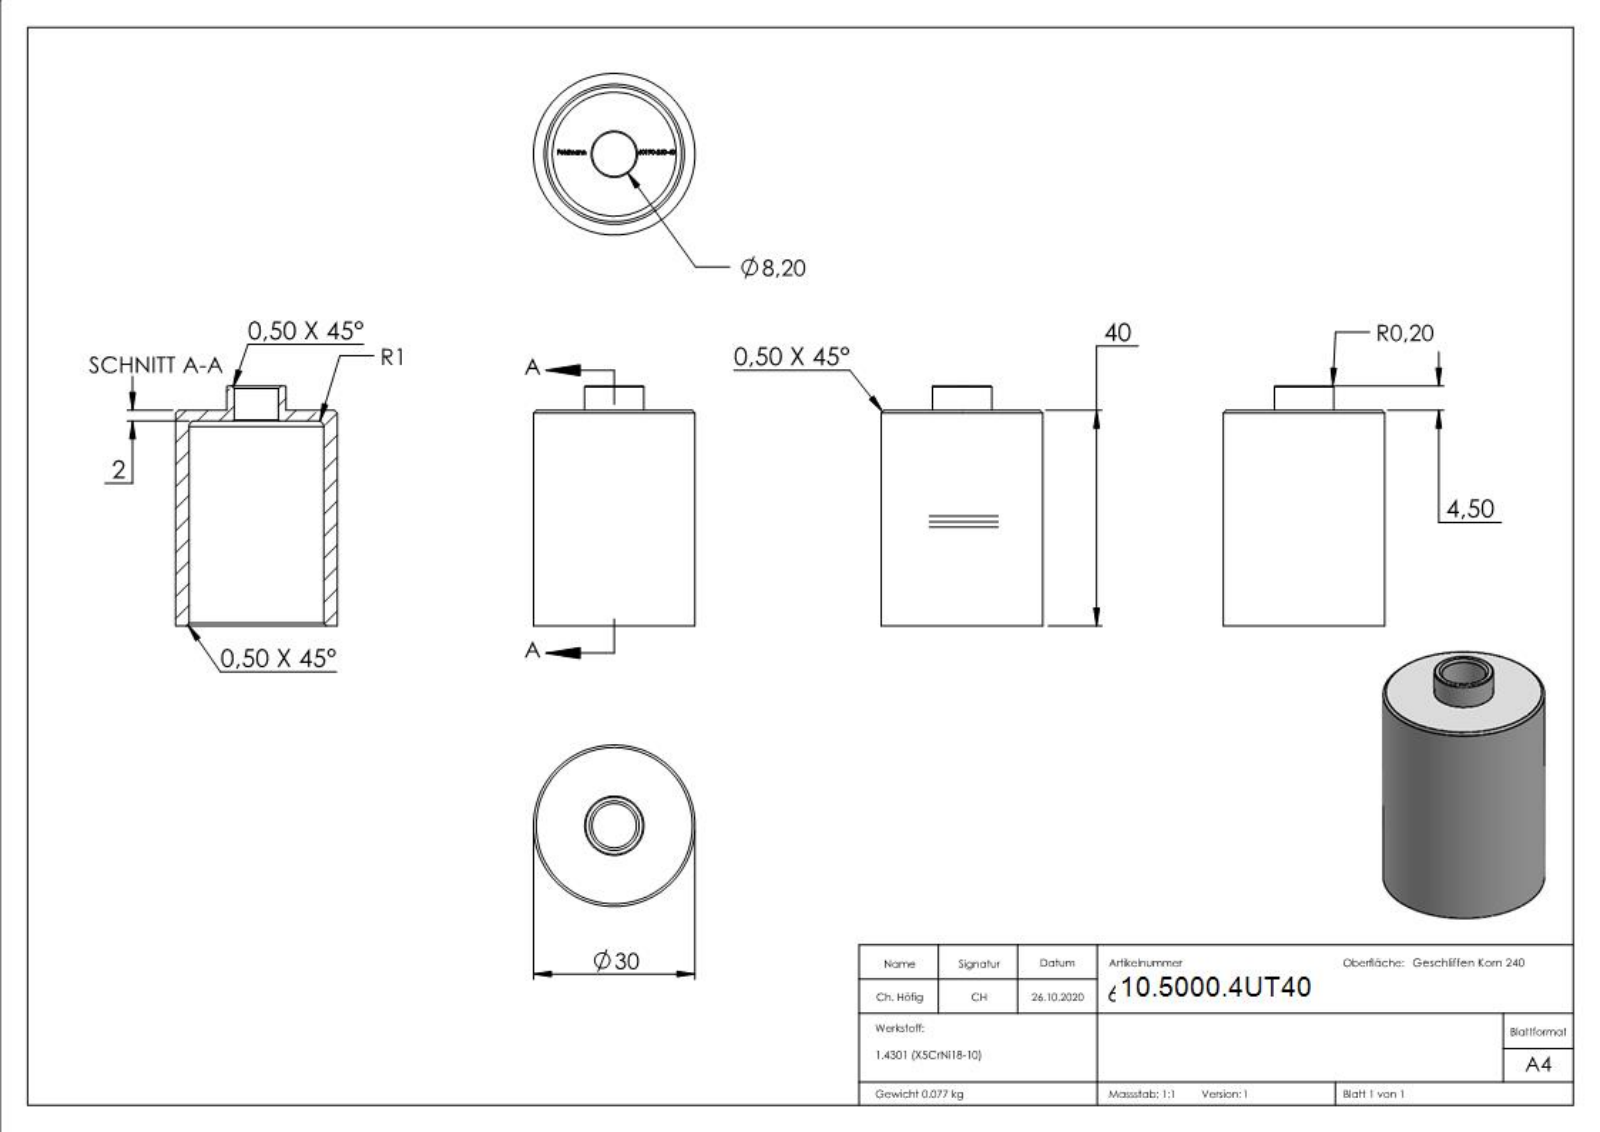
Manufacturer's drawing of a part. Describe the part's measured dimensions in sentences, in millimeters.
The part is named "60190-240-40". Its 3-D file was written by "SolidWorks 2018 (CONFIG_CONTROL_DESIGN)". It is 1 solid with 269 faces: 141 planar, 8 cylindrical and 120 other. Overall it measures 44.5 by 30 by 30 millimeters. Its volume is 9 696 cubic millimeters and its surface area 8 295 square millimeters. Round holes: 1 of diameter 8.2, 1 of diameter 25. Round bosses or shafts: 1 of diameter 30, 1 of diameter 11. The main face-to-face distances are 2, 38, 40, 44.5, 6.5, 4.5, 38.1, 1.9, 6.4, 1.78.
